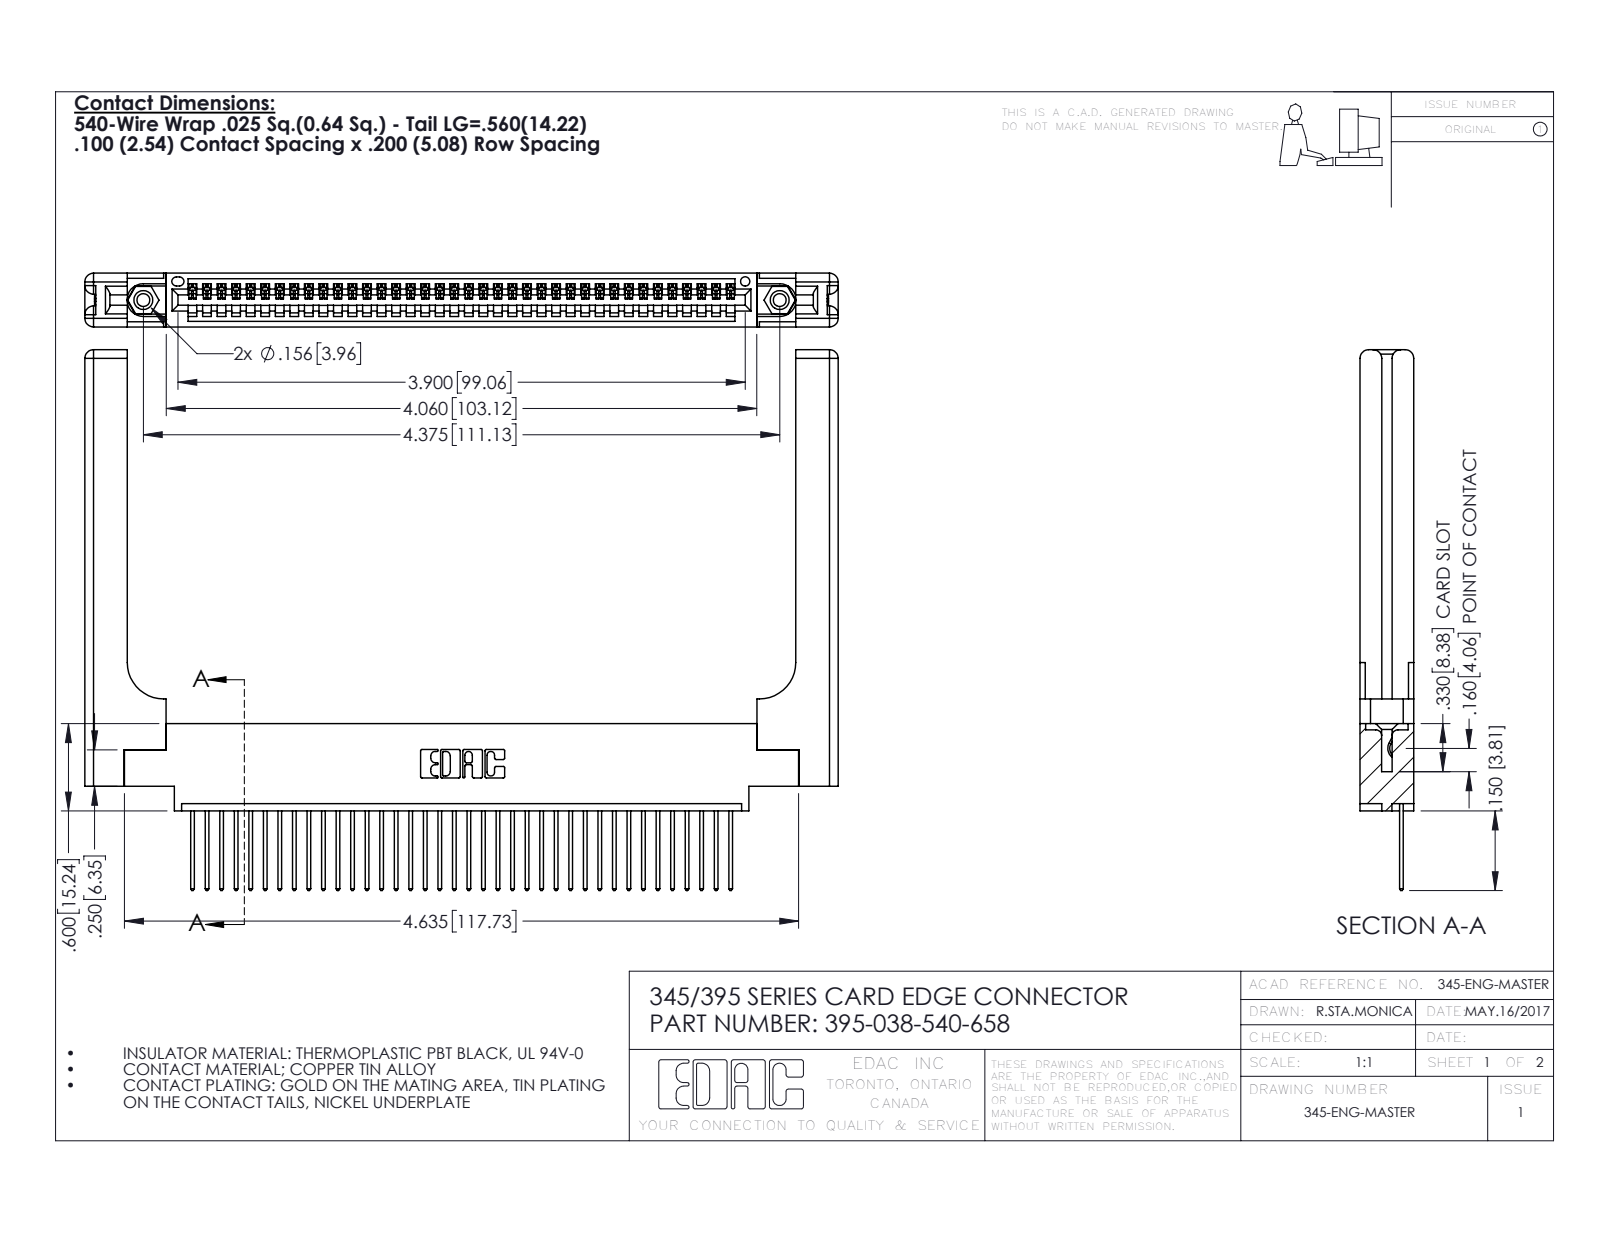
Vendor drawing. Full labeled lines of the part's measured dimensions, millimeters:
Part name (STEP PRODUCT): 345-220-058_345-220-058; 345-250-001_345-250-001-102; 395-038-540-658; 345-292-001_345-293-140 (+1 more)
STEP written by: SolidWorks 2016 (CONFIG_CONTROL_DESIGN)
Units: millimetres
Bodies: 43 solids, 2590 faces (1752 planar, 778 cylindrical, 60 other)
Overall size (bounding box): 131.5 × 94.4 × 9.4
Volume: 20 910 mm³ · Surface area: 22 230 mm²
Round holes (diameter × count): ⌀2.3 ×2, ⌀3.2 ×2, ⌀4 ×2, ⌀1.6 ×1
Round bosses / shafts (diameter × count): ⌀3.9 ×2
Partial cylindrical surfaces — rounded edges, fillets, slot ends (radius × count): R0.2 ×76, R0.3 ×76, R0.3 ×22, R1.5 ×16, R0.2 ×6, R0.8 ×6, R0.7 ×3, R0.8 ×2
Main face-to-face distances: 9.4, 1.8, 7.6, 2.5, 6.9, 0.6, 5.1, 3.8, 3.8, 5.7
Hole centre spacings: 6.9, 105.1, 111.1
